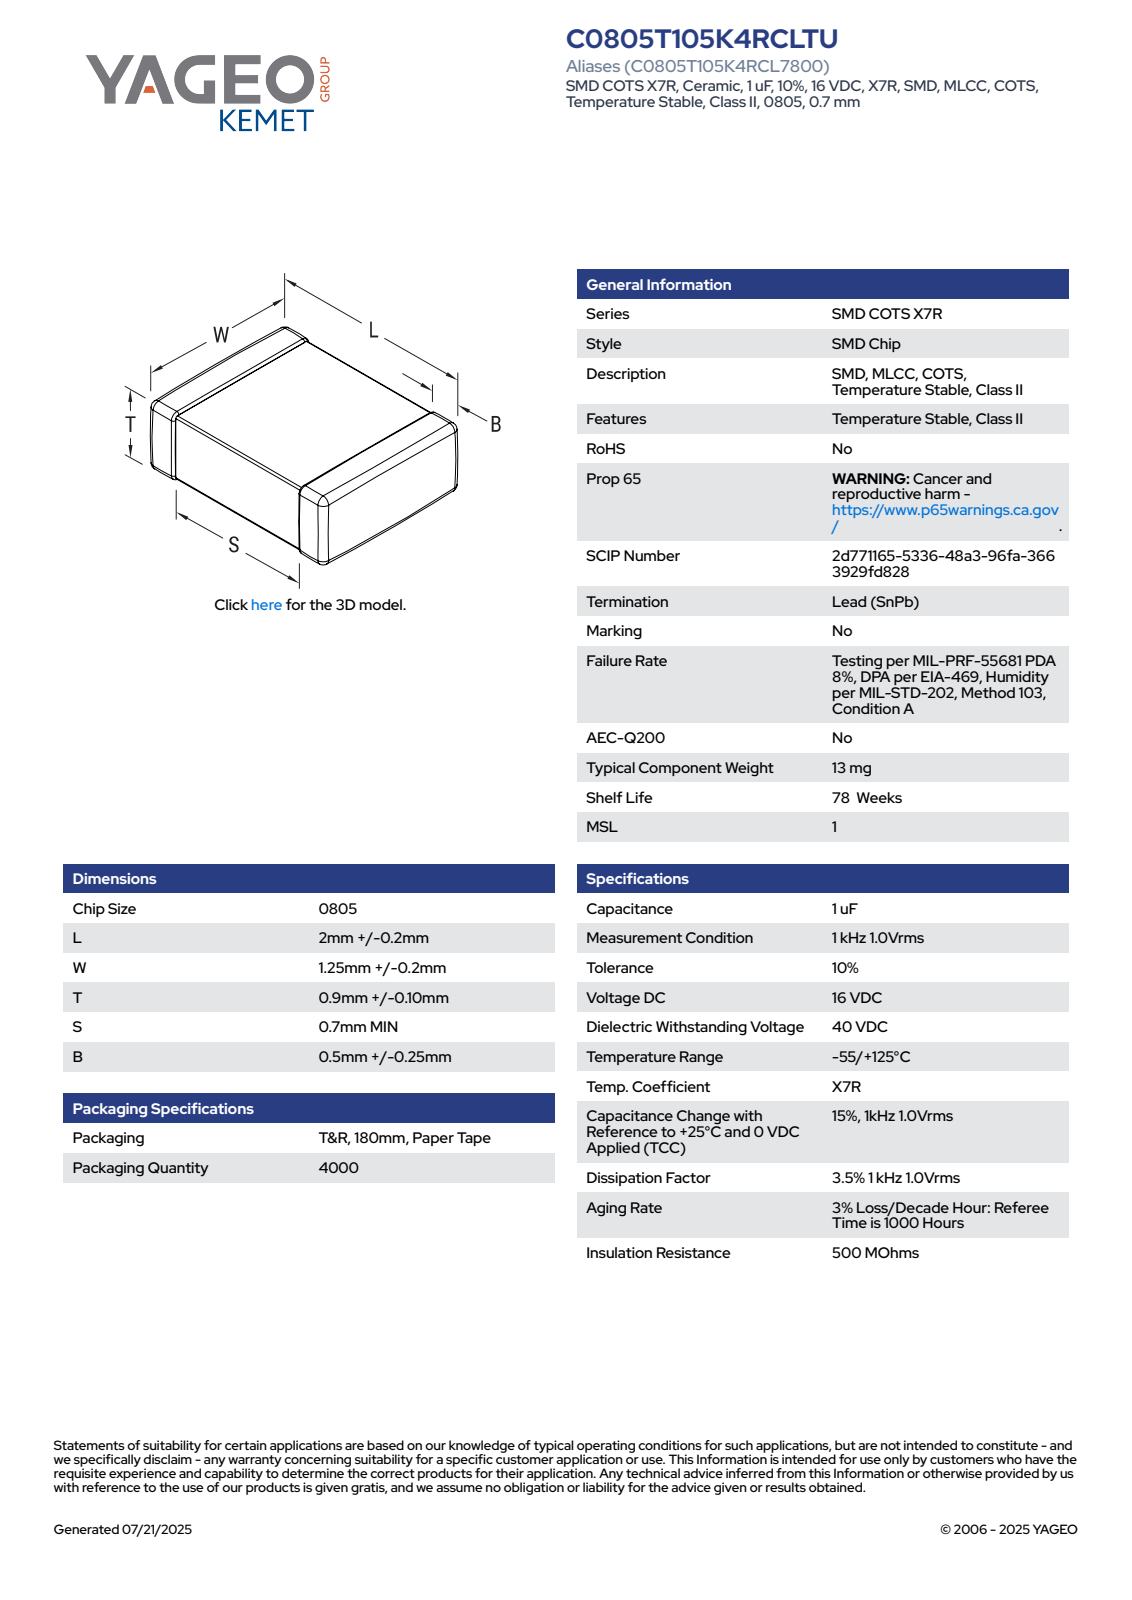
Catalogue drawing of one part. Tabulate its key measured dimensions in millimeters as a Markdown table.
| quantity | value |
| --- | --- |
| part name | CCSM_STD_0805_L2.2W1.45T1B0.75 |
| STEP written by | SolidWorks 2014 (AUTOMOTIVE_DESIGN) |
| units | millimeters |
| bodies | 4 solids, 125 faces (71 planar, 38 cylindrical, 16 other) |
| overall size | 2.2 × 1.45 × 1 |
| volume | 3 mm³ |
| surface area | 14 mm² |
| main face-to-face distances | 0.97, 1, 2.2, 1.45, 1.42, 0.94, 1.39, 0.7, 0.72, 0.73 |
